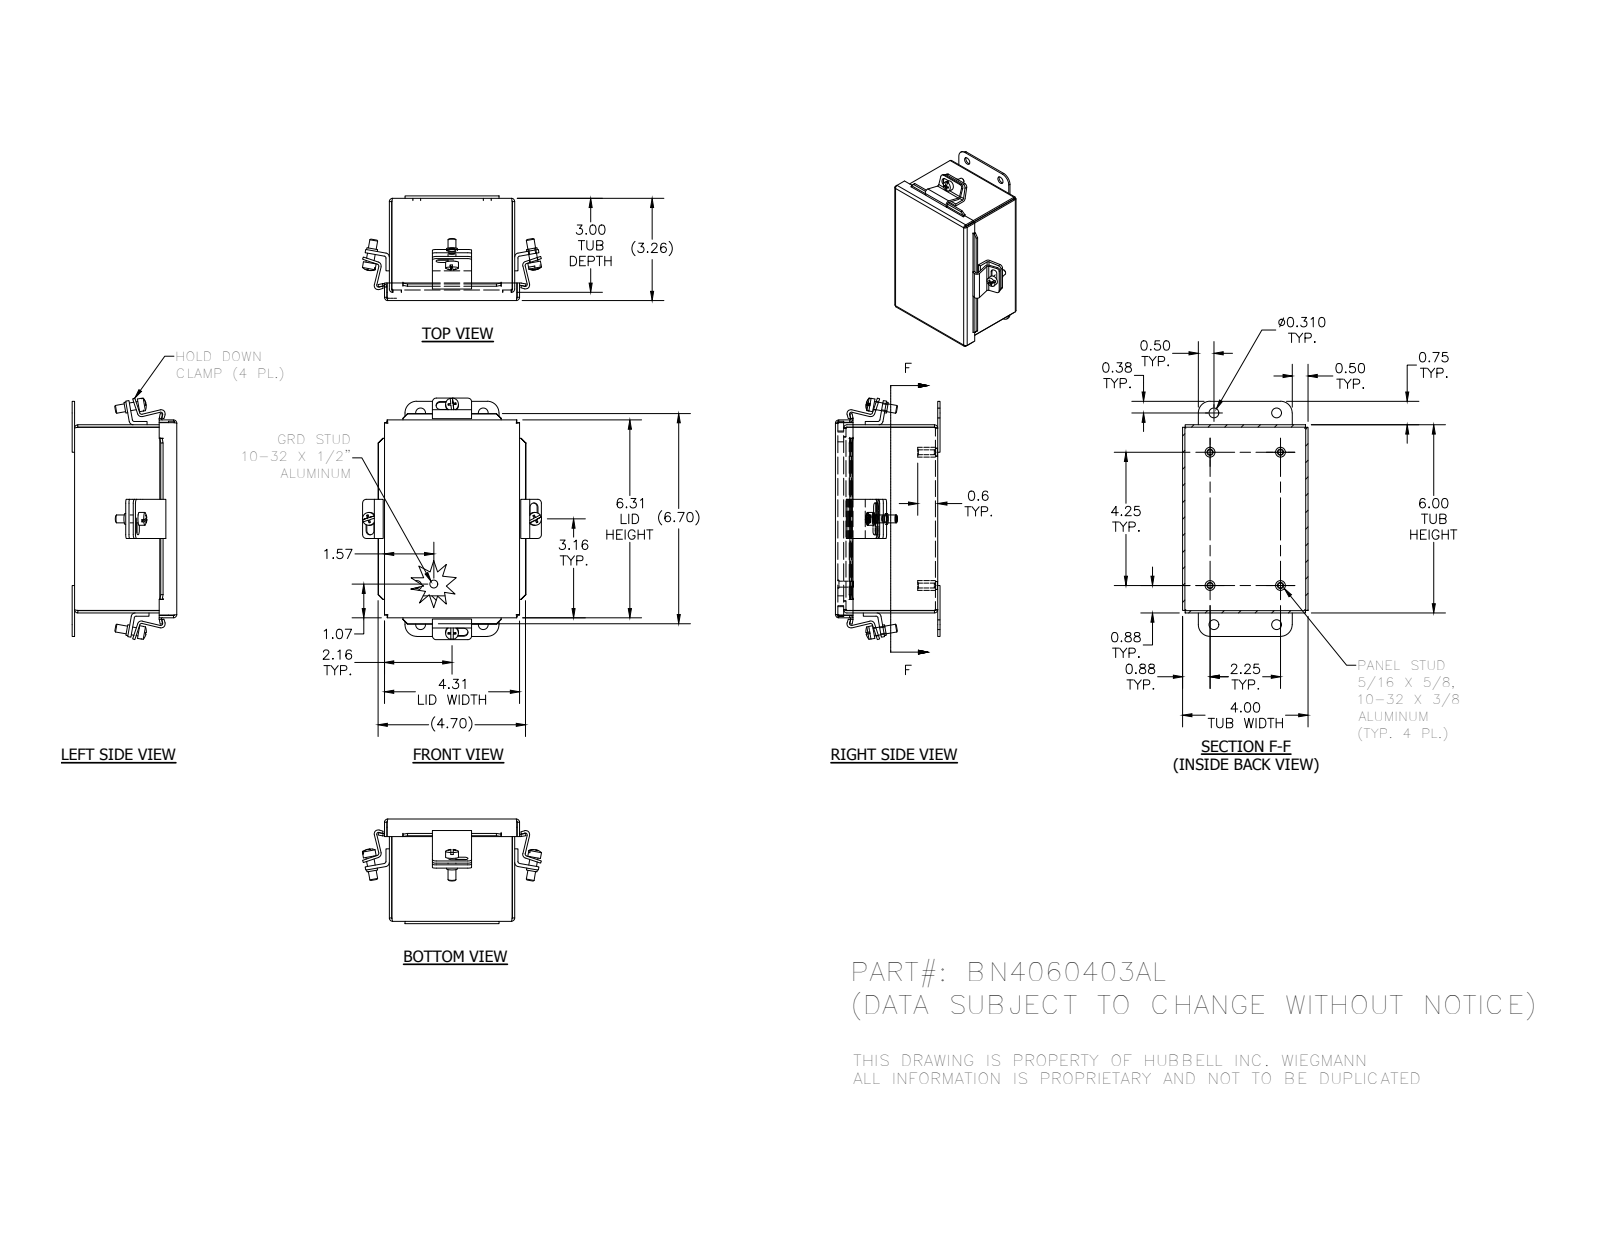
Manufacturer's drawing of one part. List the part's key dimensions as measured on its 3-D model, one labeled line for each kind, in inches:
Part name (STEP PRODUCT): BN4060403ALBKP_1; 316160_1; BN4060403AL; 38830_1 (+6 more)
STEP written by: SolidWorks 2014 (AUTOMOTIVE_DESIGN)
Units: inches
Bodies: 23 solids, 533 faces (295 planar, 176 cylindrical, 62 other)
Overall size (bounding box): 7.706 × 5.711 × 3.336
Volume: 13.59 in³ · Surface area: 344.2 in²
Round holes (diameter × count): ⌀0.156 ×4, ⌀0.196 ×4, ⌀0.25 ×4, ⌀0.31 ×4
Round bosses / shafts (diameter × count): ⌀0.25 ×5, ⌀0.41 ×4, ⌀0.344 ×4, ⌀0.313 ×4, ⌀0.19 ×1
Partial cylindrical surfaces — rounded edges, fillets, slot ends (radius × count): R0.031 ×16, R0.105 ×16, R0.125 ×16, R0.063 ×12, R0.126 ×12, R0.133 ×8, R0.375 ×4
Main face-to-face distances: 0.074, 3.187, 3.926, 3.261, 3.113, 0.261, 5.926, 2.926, 4, 0.187
Hole centre spacings: 1.256, 5.502, 2, 2.25, 2.465, 2.466, 4.25, 4.809
